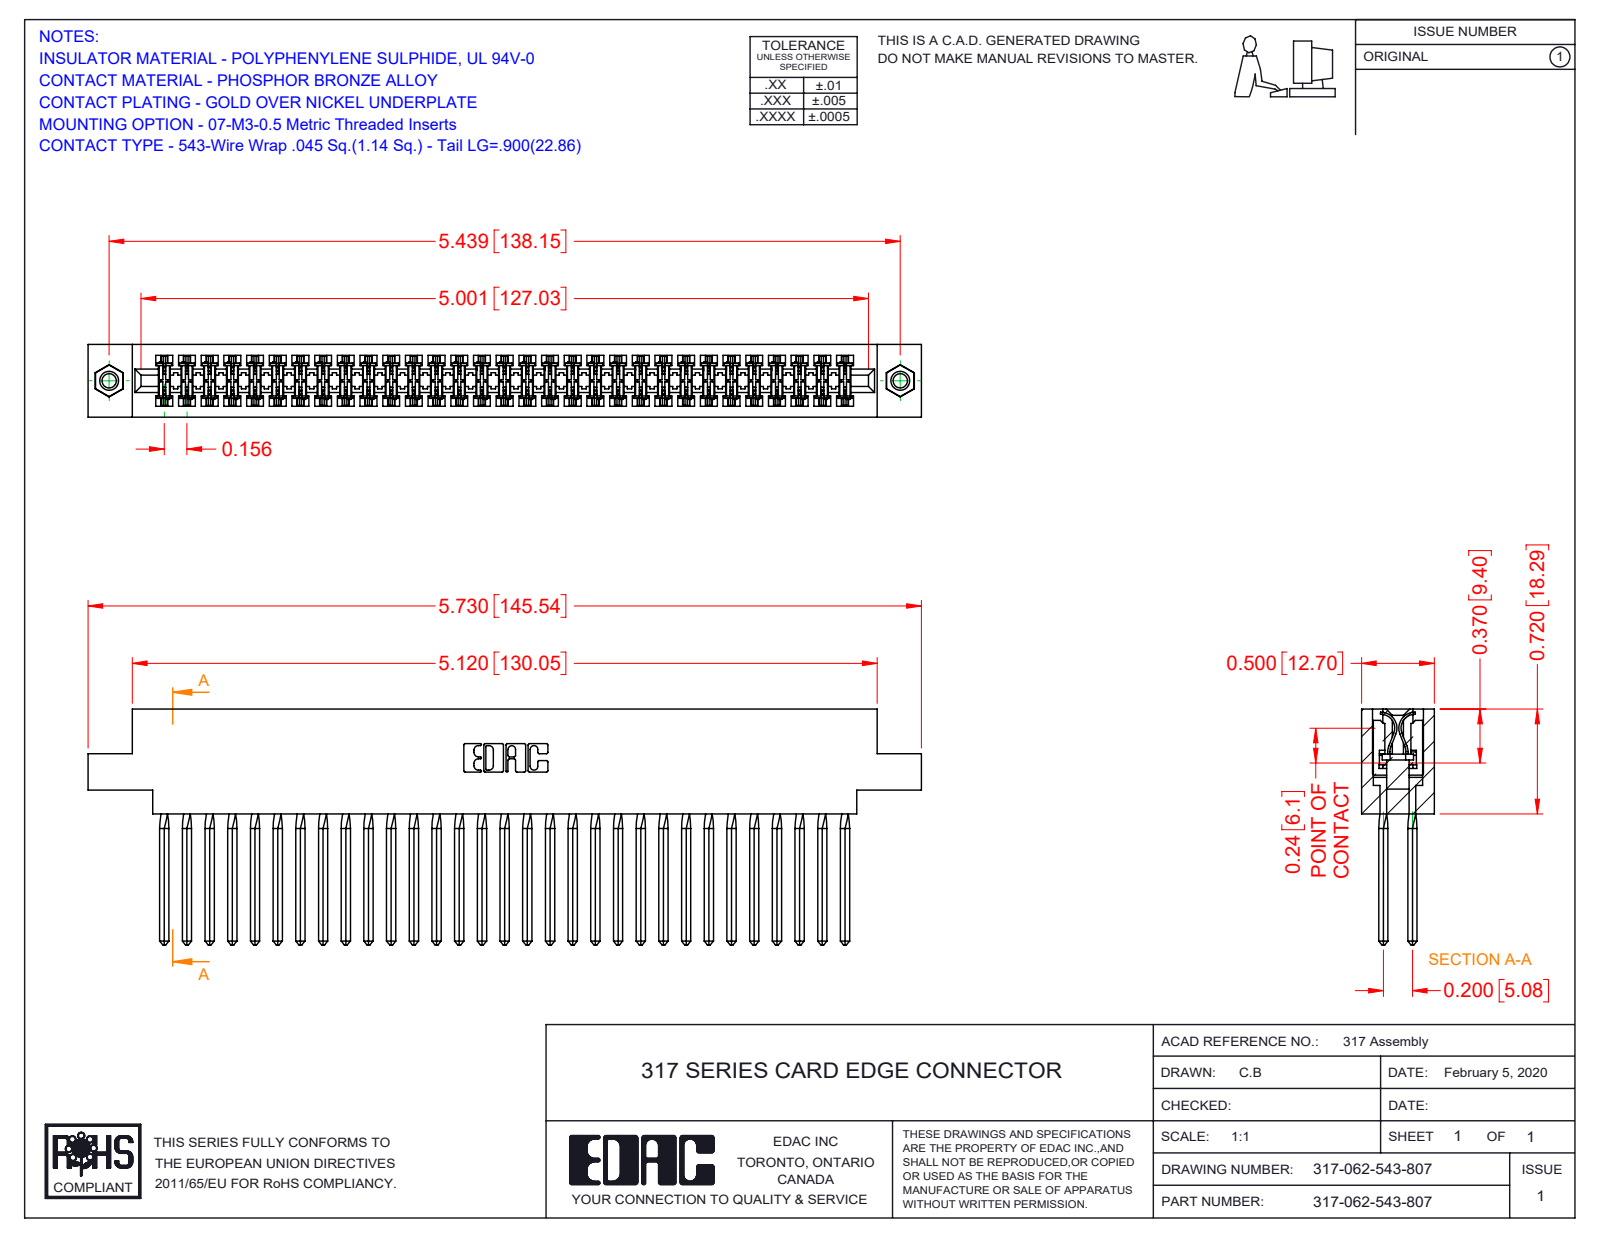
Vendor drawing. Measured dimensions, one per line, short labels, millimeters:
name: 317-062-543-807; 345-250-001_345-250-005-103; 317 Part_.156 Dia - TI; 317-290-001_543
written by: SolidWorks 2016 (CONFIG_CONTROL_DESIGN)
unit: mm
bodies: 65 solids, 5680 faces (4616 planar, 800 cylindrical, 264 other)
size: 145.5 × 41.1 × 12.7
volume: 24 350 mm³; area: 36 540 mm²
holes: 2× ⌀2.5, 2× ⌀3.2, 2× ⌀4
bosses: 2× ⌀3.9
rounds: 124× R0.4, 22× R0.3, 6× R0.2, 6× R0.8, 3× R0.7, 2× R2.4, 2× R2.5, 2× R2.8
face distances: 12.7, 1.9, 10.8, 8.9, 2.8, 5, 2.4, 5.1, 2.9, 3.3
hole spacings: 138.2
